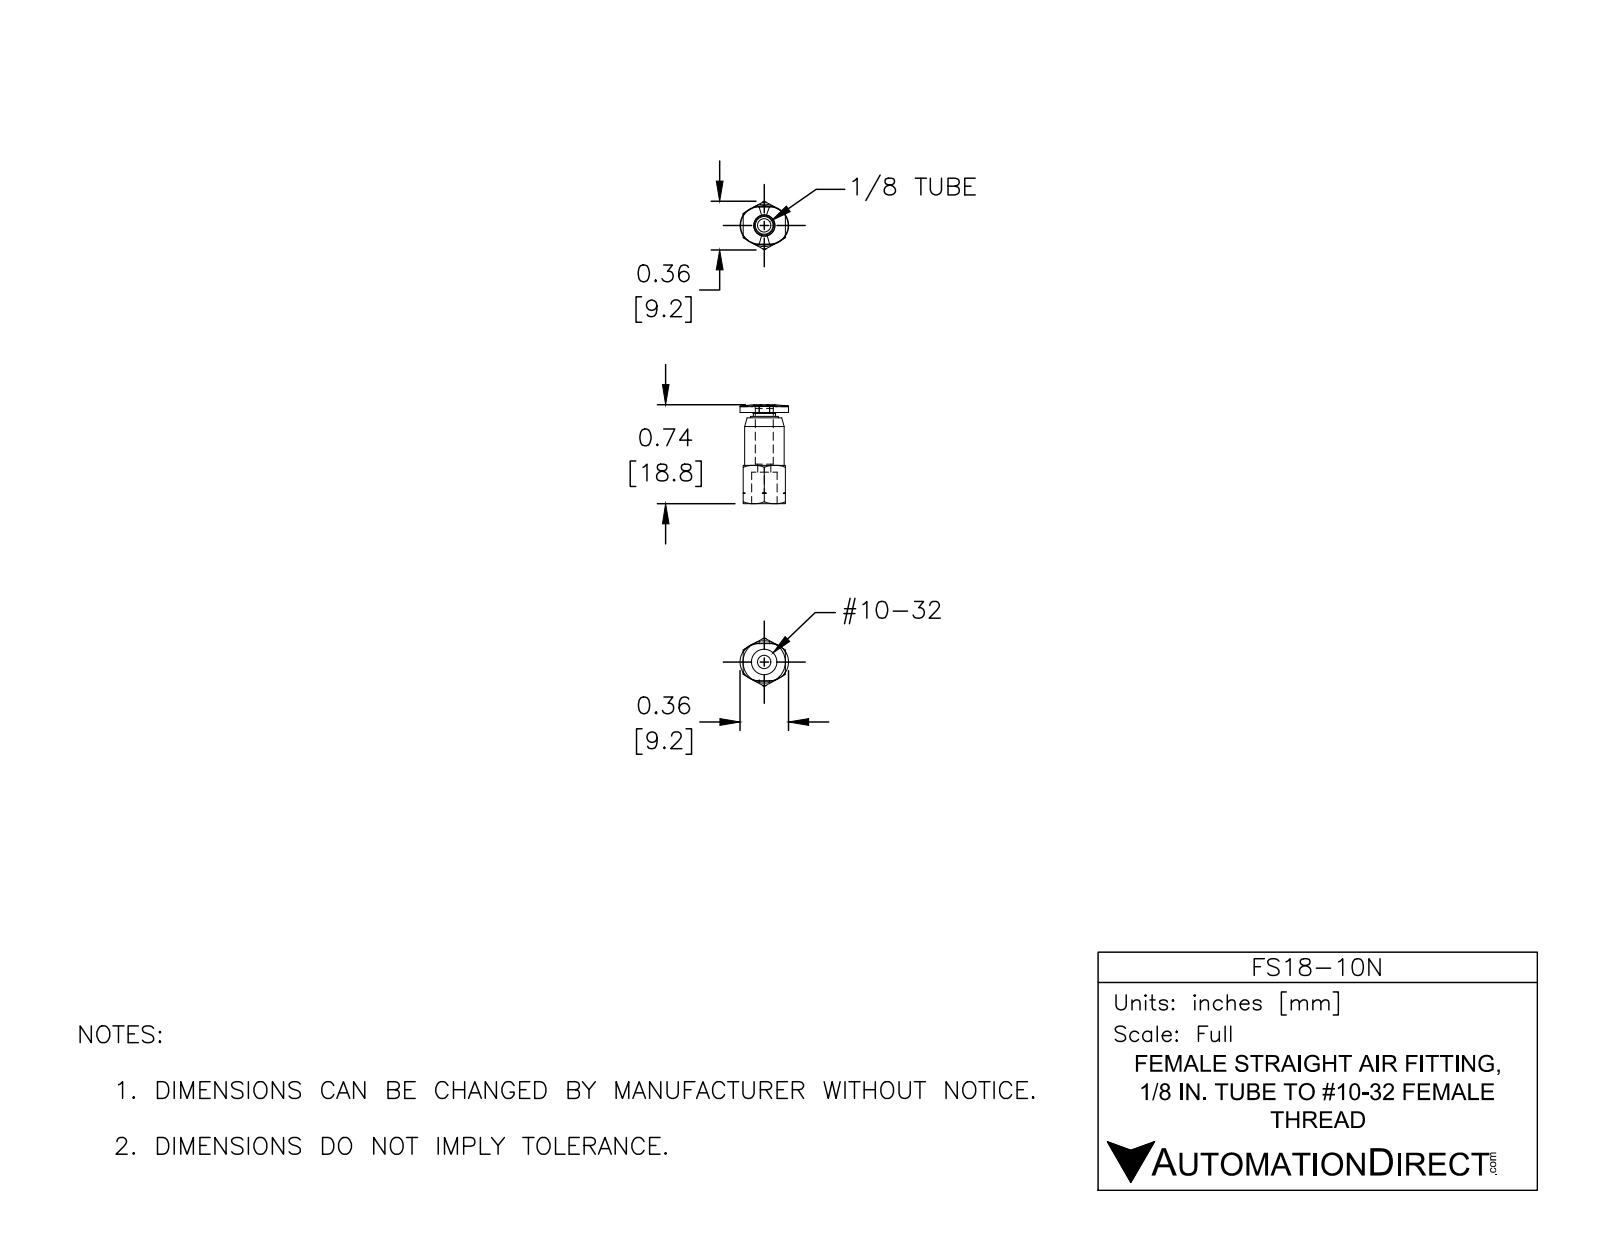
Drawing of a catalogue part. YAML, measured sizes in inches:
part_name: "FS18-10N"
step_written_by: "SolidWorks 2015 (CONFIG_CONTROL_DESIGN)"
units: inches
bodies: {solids: 1, faces: 78, planar: 16, cylindrical: 14, other: 48}
overall_size: [0.74, 0.364, 0.362]
volume: 0.041
surface_area: 1.316
round_holes:
  - {diameter: 0.098, count: 1}
  - {diameter: 0.134, count: 1}
  - {diameter: 0.19, count: 1}
round_bosses_or_shafts:
  - {diameter: 0.295, count: 1}
  - {diameter: 0.209, count: 1}
  - {diameter: 0.165, count: 1}
partial_cylinders:
  - {radius: 0.142, count: 2}
face_to_face_distances: [0.315, 0.681, 0.445, 0.236, 0.642, 0.406, 0.039, 0.652, 0.415, 0.03]
